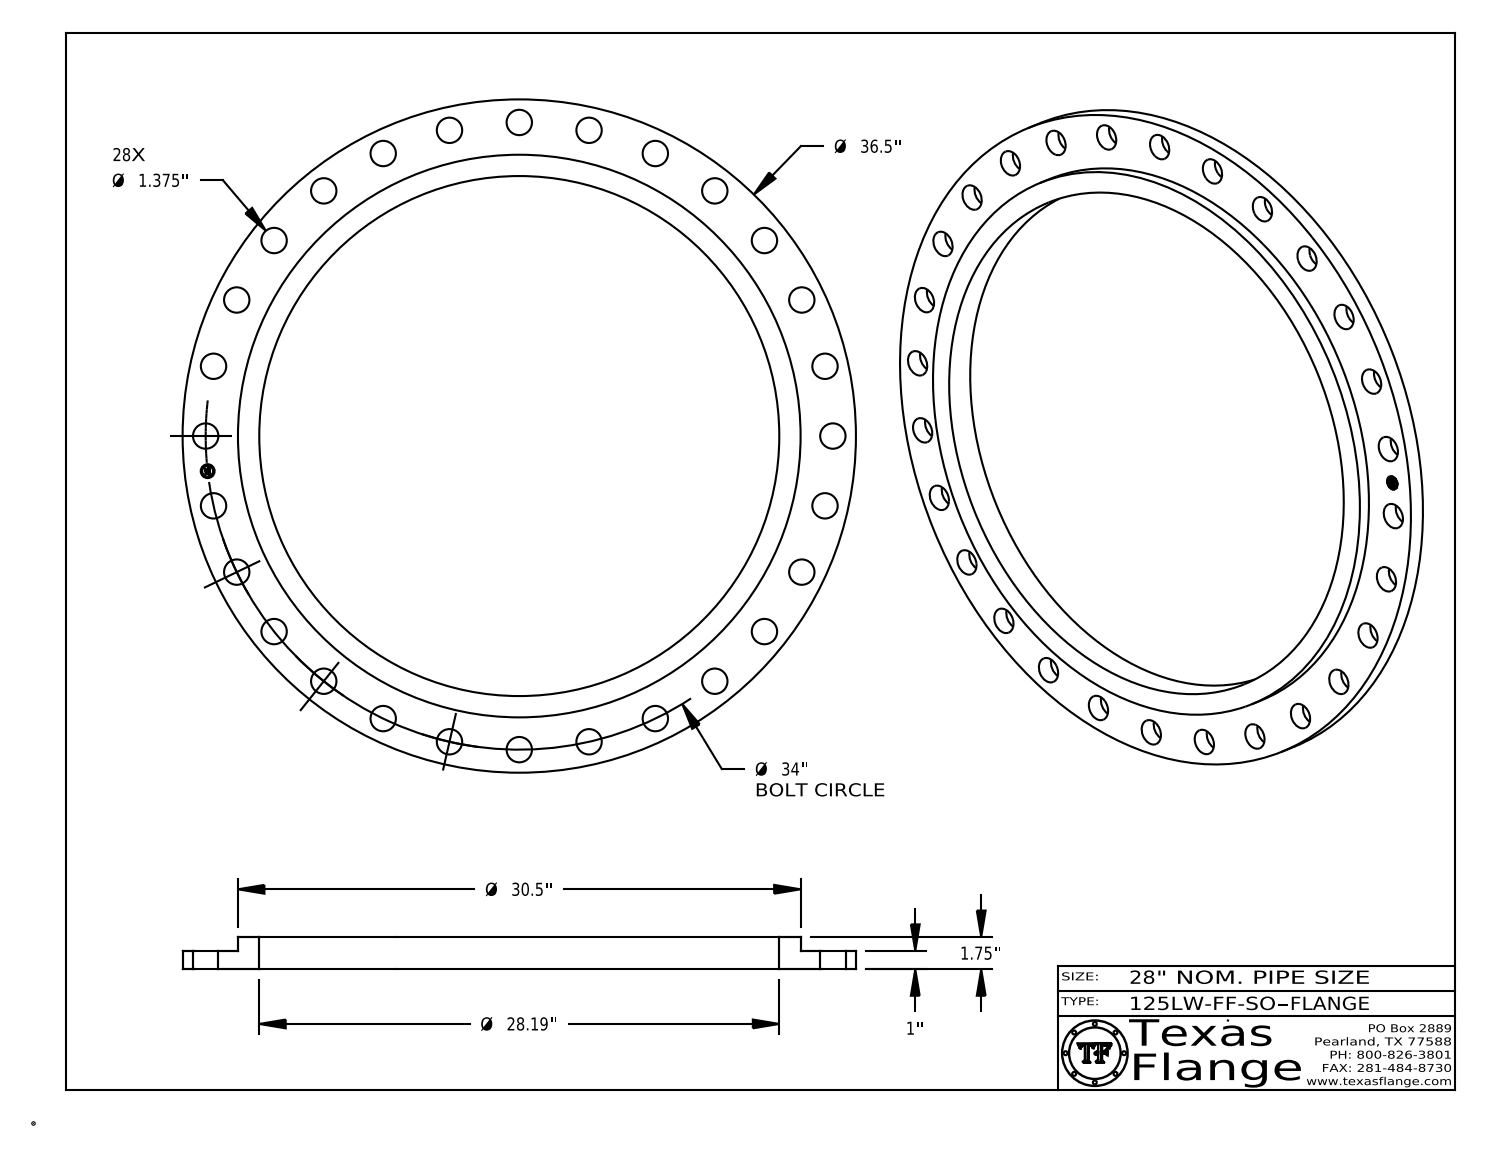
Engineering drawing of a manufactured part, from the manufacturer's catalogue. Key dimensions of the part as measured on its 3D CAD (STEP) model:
Part name (STEP PRODUCT): 125LW-FF-SO-B16.1
STEP written by: CATIA V5 STEP AP214 (AUTOMOTIVE_DESIGN)
Units: inches
Bodies: 1 solid, 450 faces (368 planar, 82 cylindrical, 0 other)
Overall size (bounding box): 36.5 × 36.5 × 1.75
Volume: 460.5 in³ · Surface area: 1 224 in²
Round holes (diameter × count): ⌀1.375 ×28, ⌀0.75 ×1, ⌀28.19 ×1
Round bosses / shafts (diameter × count): ⌀0.045 ×8, ⌀36.5 ×1, ⌀30.5 ×1, ⌀0.591 ×1
Main face-to-face distances: 1, 1.75, 0.75, 0.985, 0.015, 0.765, 0.224, 0.22, 0.041, 0.145
Hole centre spacings: 3.807, 7.566, 30.633, 33.786, 17, 11.23, 18.089, 21.198
